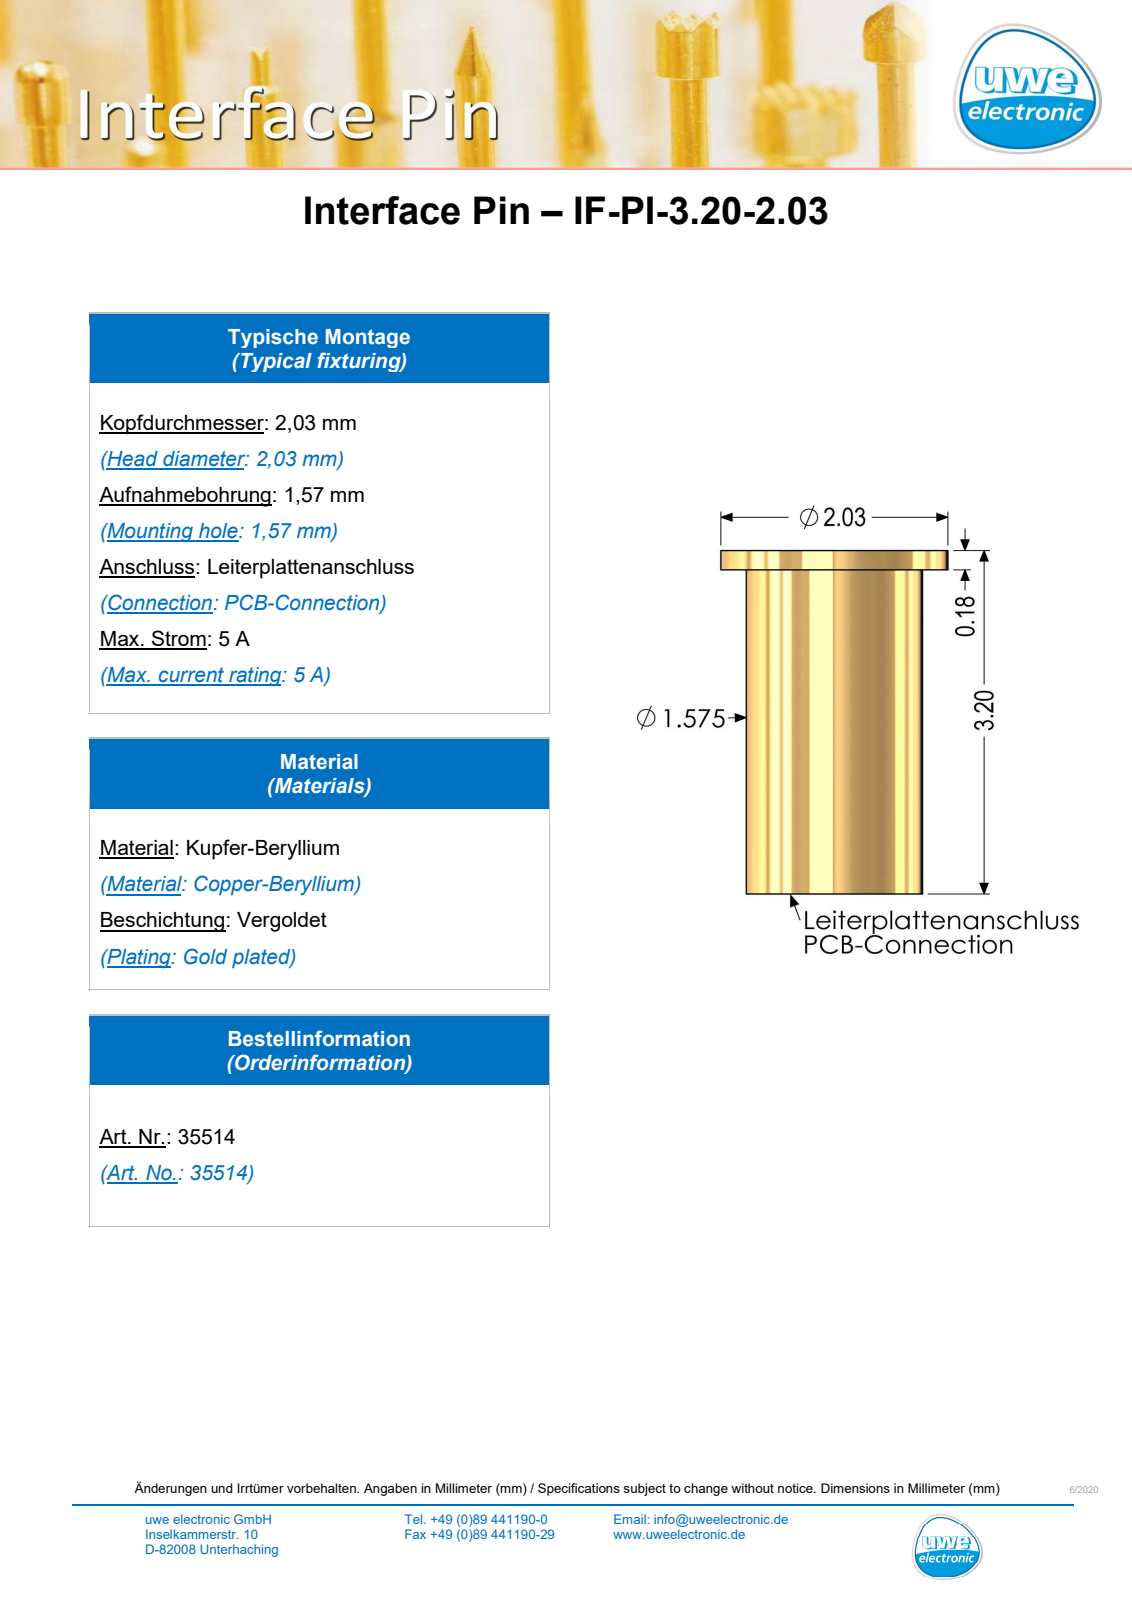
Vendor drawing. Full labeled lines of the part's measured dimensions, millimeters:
Part name (STEP PRODUCT): IF-PI-3.20-2.30_2017_08_21
STEP written by: SolidWorks 2017 (AUTOMOTIVE_DESIGN)
Units: millimetres
Bodies: 1 solid, 7 faces (3 planar, 4 cylindrical, 0 other)
Overall size (bounding box): 3.2 × 2.03 × 2.03
Volume: 6 mm³ · Surface area: 23 mm²
Round bosses / shafts (diameter × count): ⌀2.03 ×1, ⌀1.58 ×1
Main face-to-face distances: 3.2, 3.02
